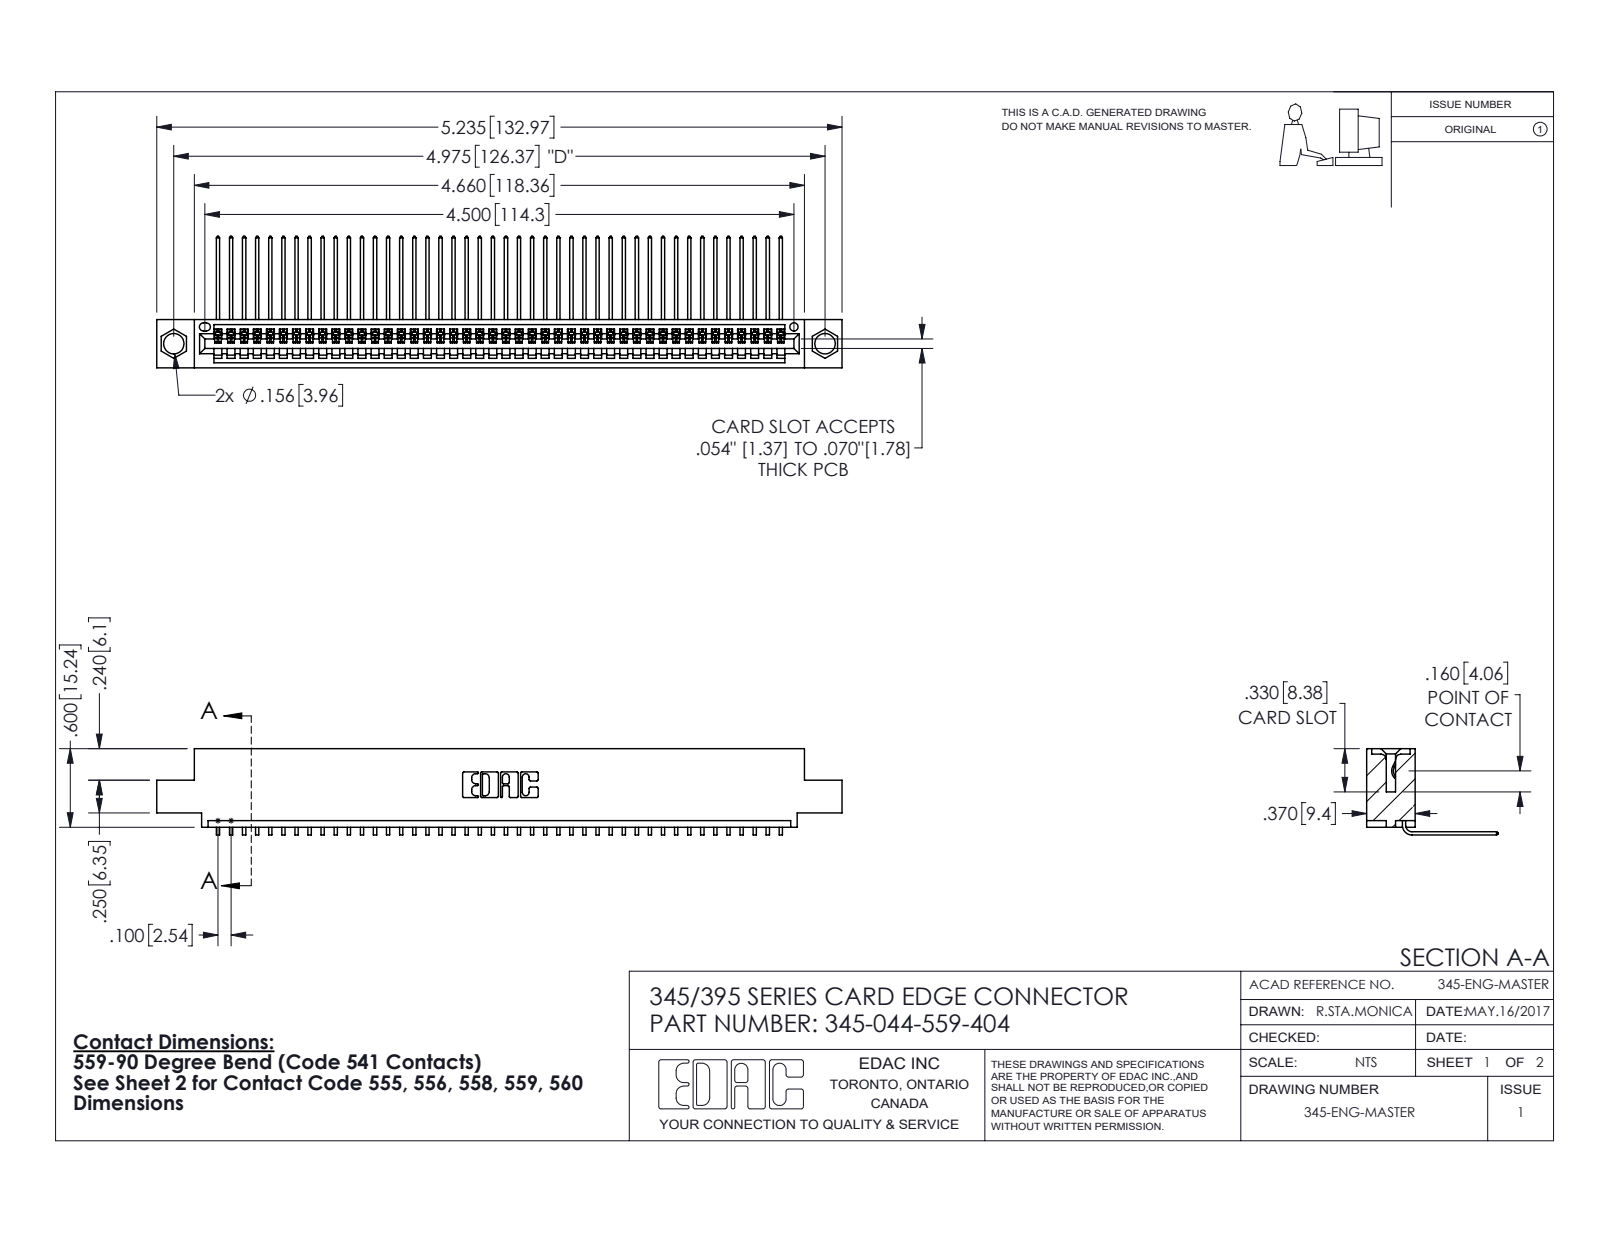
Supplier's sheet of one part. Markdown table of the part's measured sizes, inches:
| quantity | value |
| --- | --- |
| part name | 345-044-559-404; 345-292-001_558 559 Tail - 1; 345 Part_0.110 Offset - 0.156 Dia-TH |
| STEP written by | SolidWorks 2016 (CONFIG_CONTROL_DESIGN) |
| units | inches |
| bodies | 45 solids, 2770 faces (1932 planar, 838 cylindrical, 0 other) |
| overall size | 5.235 × 1.005 × 0.659 |
| volume | 0.771 in³ |
| surface area | 27.23 in² |
| round holes (diameter × count) | 0.156 × 2, 0.064 × 1 |
| partial cylindrical surfaces (radius × count) | 0.006 × 88, 0.01 × 22, 0.007 × 6, 0.031 × 6, 0.026 × 3, 0.031 × 2, 0.04 × 2, 0.014 × 1 |
| main face-to-face distances | 0.072, 0.298, 0.37, 0.2, 0.098, 0.272, 0.025, 0.225, 0.149, 0.072 |
| hole center spacings | 0.27, 4.739, 4.975 |
